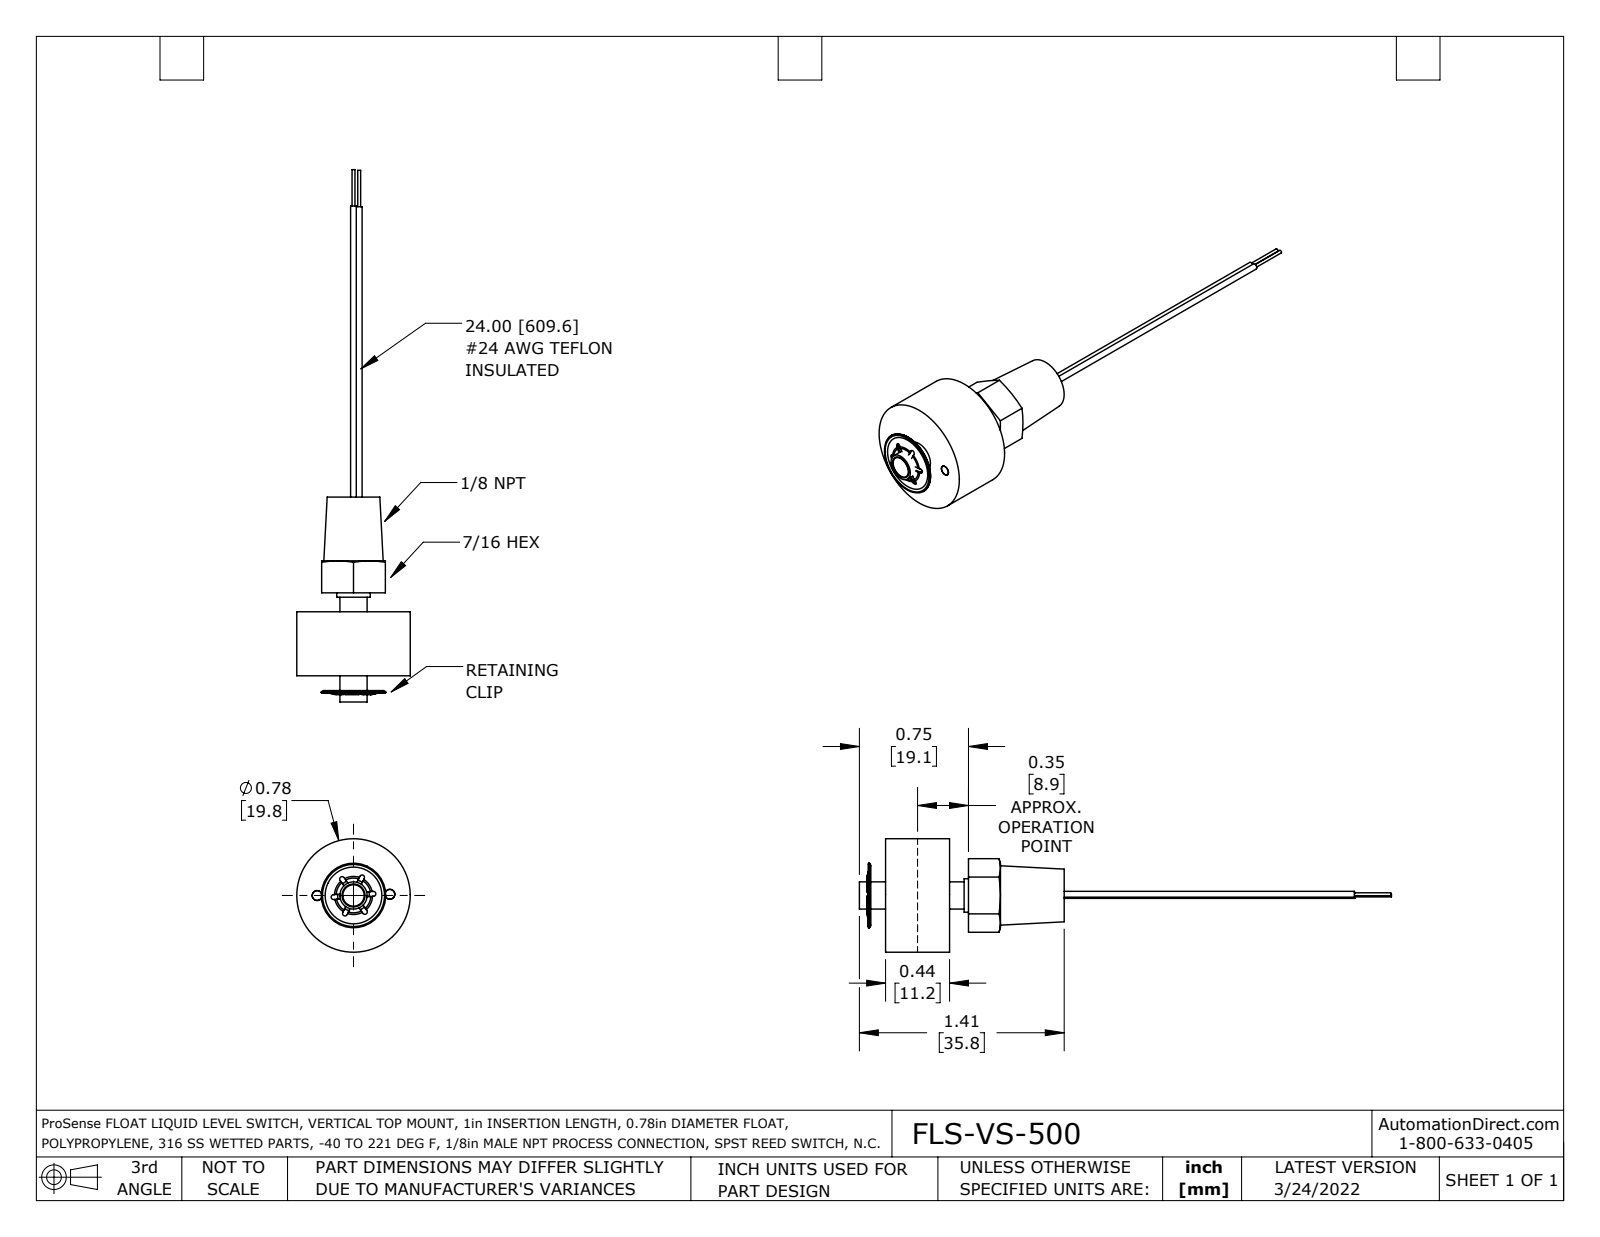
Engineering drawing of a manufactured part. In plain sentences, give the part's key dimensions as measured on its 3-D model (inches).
The part is named "ADM4035 nc fxt". Its 3-D file was written by "SolidWorks 2017 (AUTOMOTIVE_DESIGN)". It is 11 solids with 139 faces: 50 planar, 51 cylindrical and 38 other. Overall it measures 3.658 by 0.78 by 0.78 inches. Its volume is 0.28 cubic inches and its surface area 6.053 square inches. Round holes: 2 of diameter 0.068, 1 of diameter 0.147, 1 of diameter 0.187, 1 of diameter 0.218. Round bosses or shafts: 2 of diameter 0.063, 2 of diameter 0.04, 2 of diameter 0.02, 1 of diameter 0.78, 1 of diameter 0.444, 1 of diameter 0.23, 1 of diameter 0.158. Partial cylindrical surfaces (rounded edges, fillets, slot ends): 6 of radius 0.017, 1 of radius 0.085. The main face-to-face distances are 0.44, 0.438, 0.13, 0.57, 0.658, 0.788, 1.228, 0.03, 1.408, 0.75. The hole center spacings are 0.25, 0.5.
